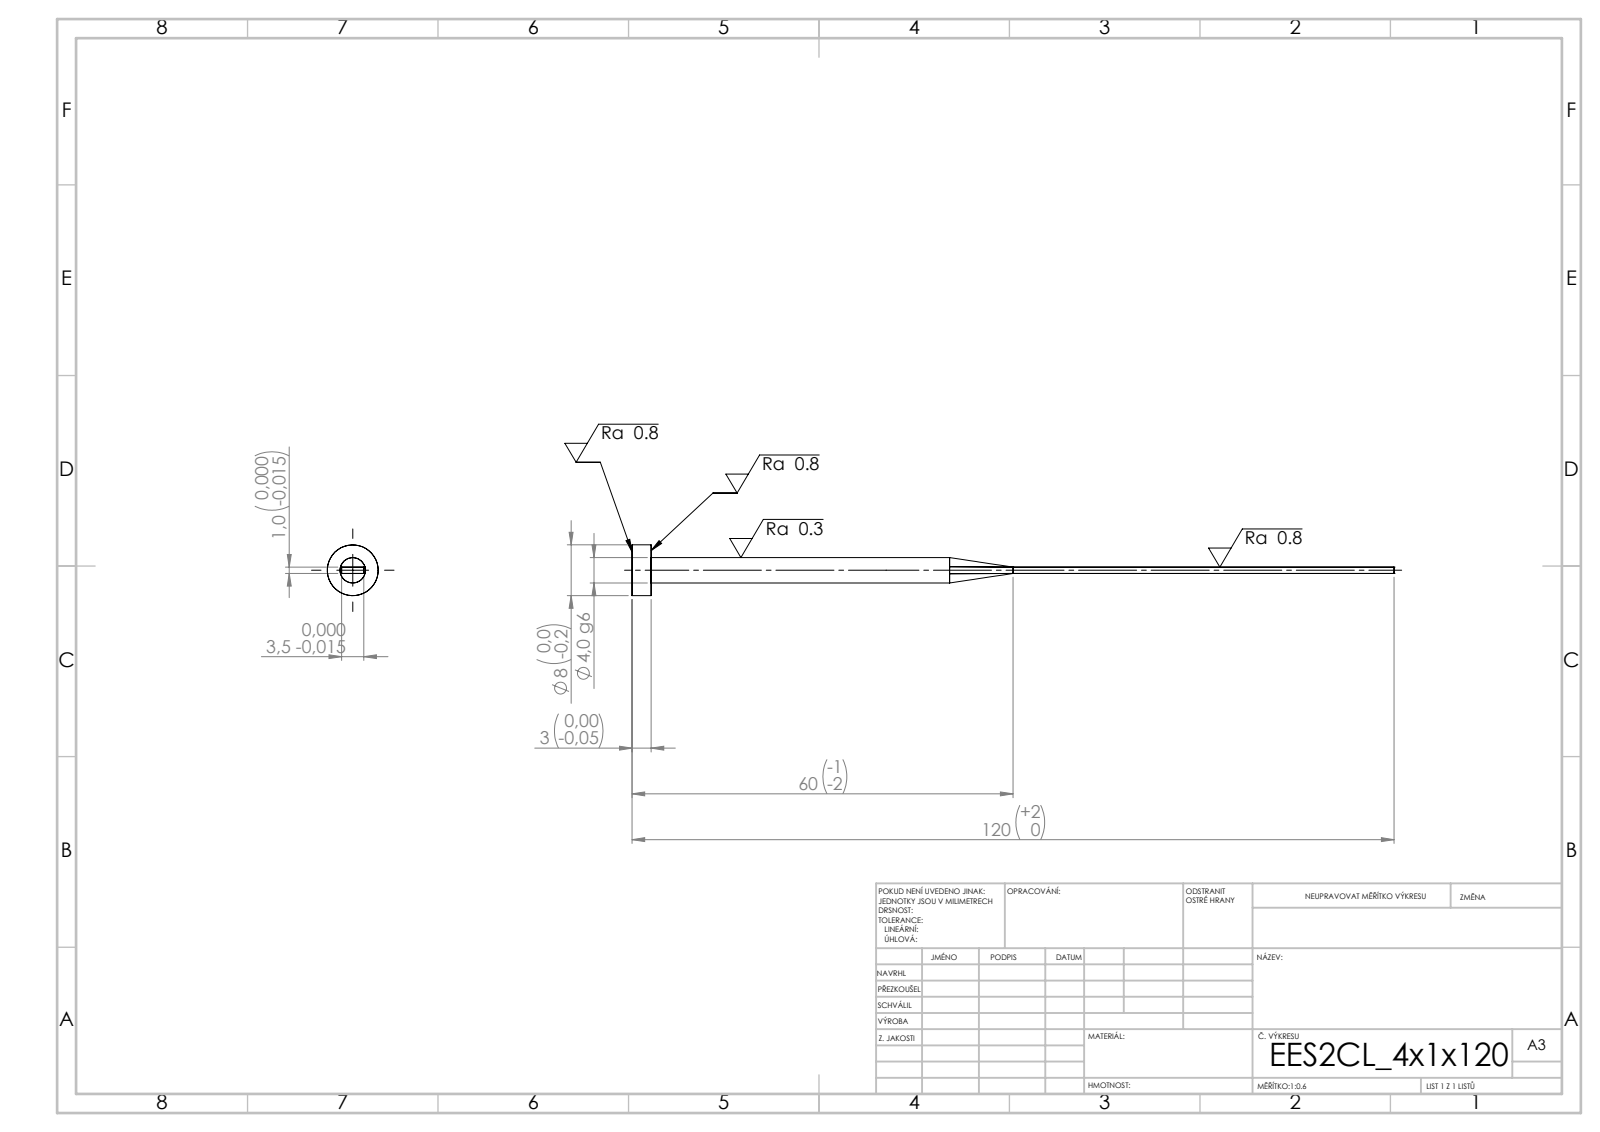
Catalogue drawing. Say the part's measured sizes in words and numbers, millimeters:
Its 3-D file was written by "SolidWorks 2019 (CONFIG_CONTROL_DESIGN)". It is 1 solid with 15 faces: 7 planar, 4 cylindrical and 4 other. Overall it measures 120 by 8 by 8 millimeters. Its volume is 1 028 cubic millimeters and its surface area 1 402 square millimeters. Round bosses or shafts: 1 of diameter 8, 1 of diameter 4. The main face-to-face distances are 1, 3.5, 3, 120, 117.
